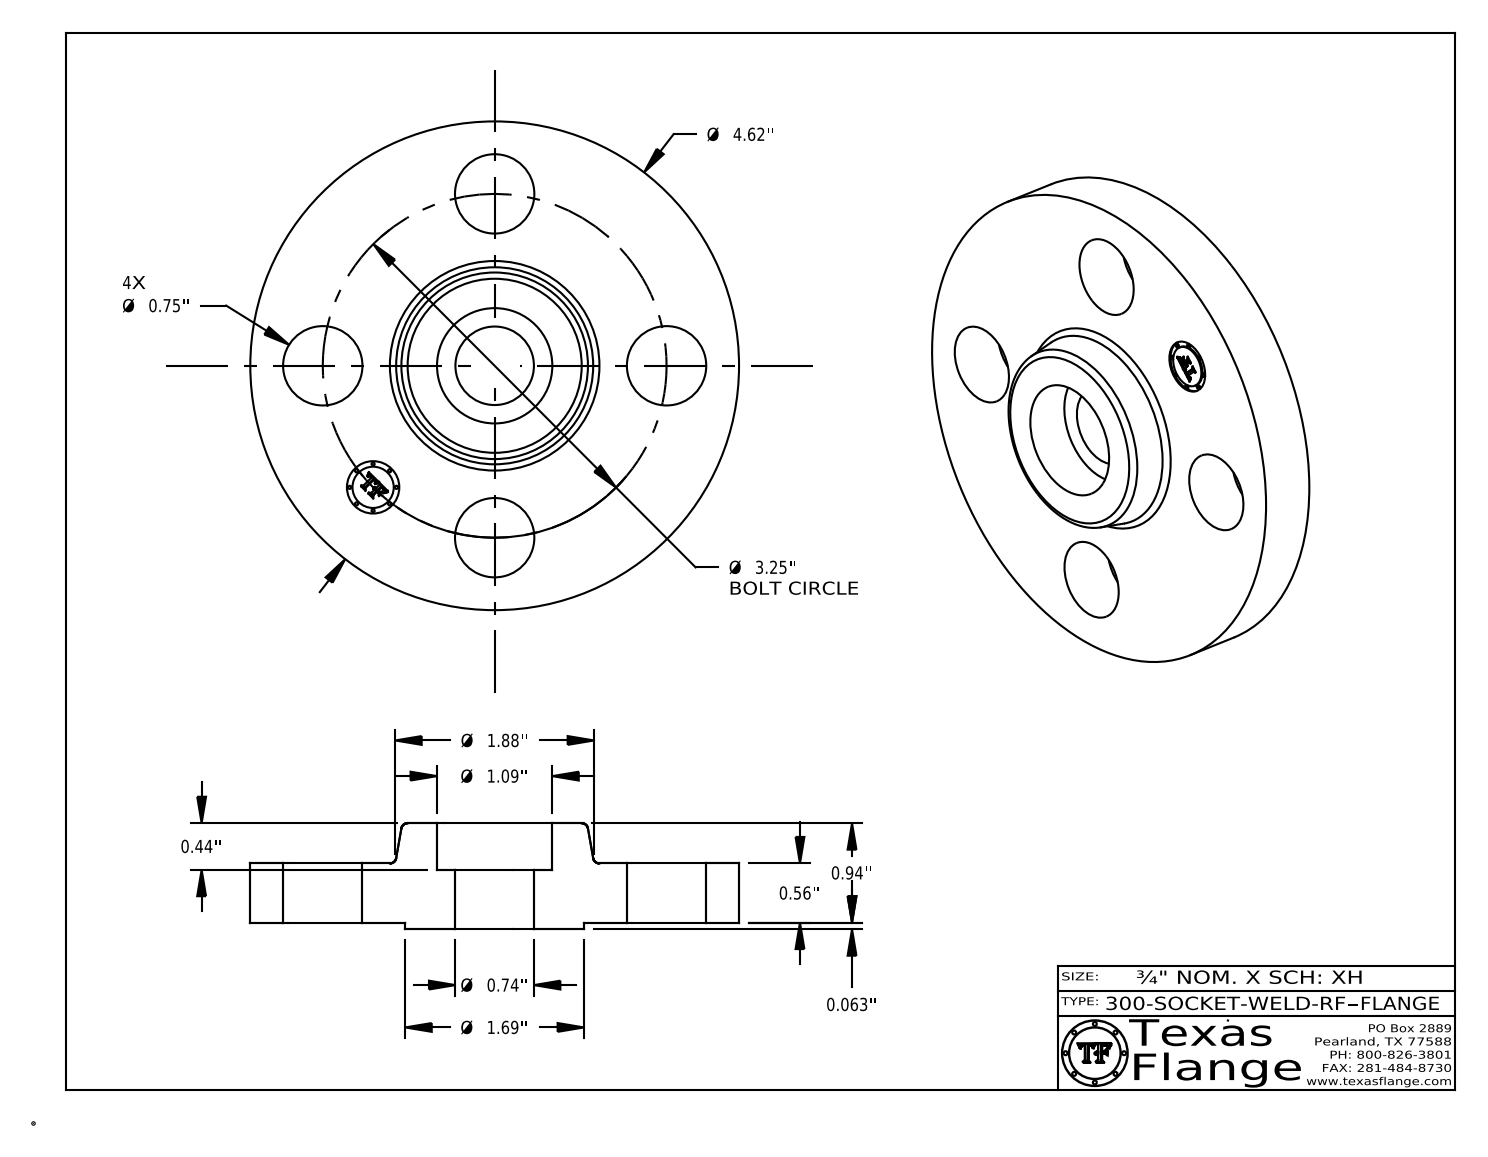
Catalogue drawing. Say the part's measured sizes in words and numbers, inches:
The part is named "300-SOCKET-WELD-RF". Its 3-D file was written by "CATIA V5 STEP AP214 (AUTOMOTIVE_DESIGN)". It is 1 solid with 412 faces: 370 planar, 36 cylindrical and 6 other. Overall it measures 4.62 by 4.62 by 1.003 inches. Its volume is 8.865 cubic inches and its surface area 47.4 square inches. Round holes: 4 of diameter 0.75, 1 of diameter 0.495, 1 of diameter 0.742, 1 of diameter 1.09. Round bosses or shafts: 8 of diameter 0.03, 1 of diameter 4.62, 1 of diameter 1.69, 1 of diameter 0.39. The main face-to-face distances are 0.56, 0.063, 0.622, 1.003, 0.94, 0.38, 0.563, 0.5, 0.06, 0.44. The hole center spacings are 1.625, 2.298, 1.244, 3.003, 3.25.
